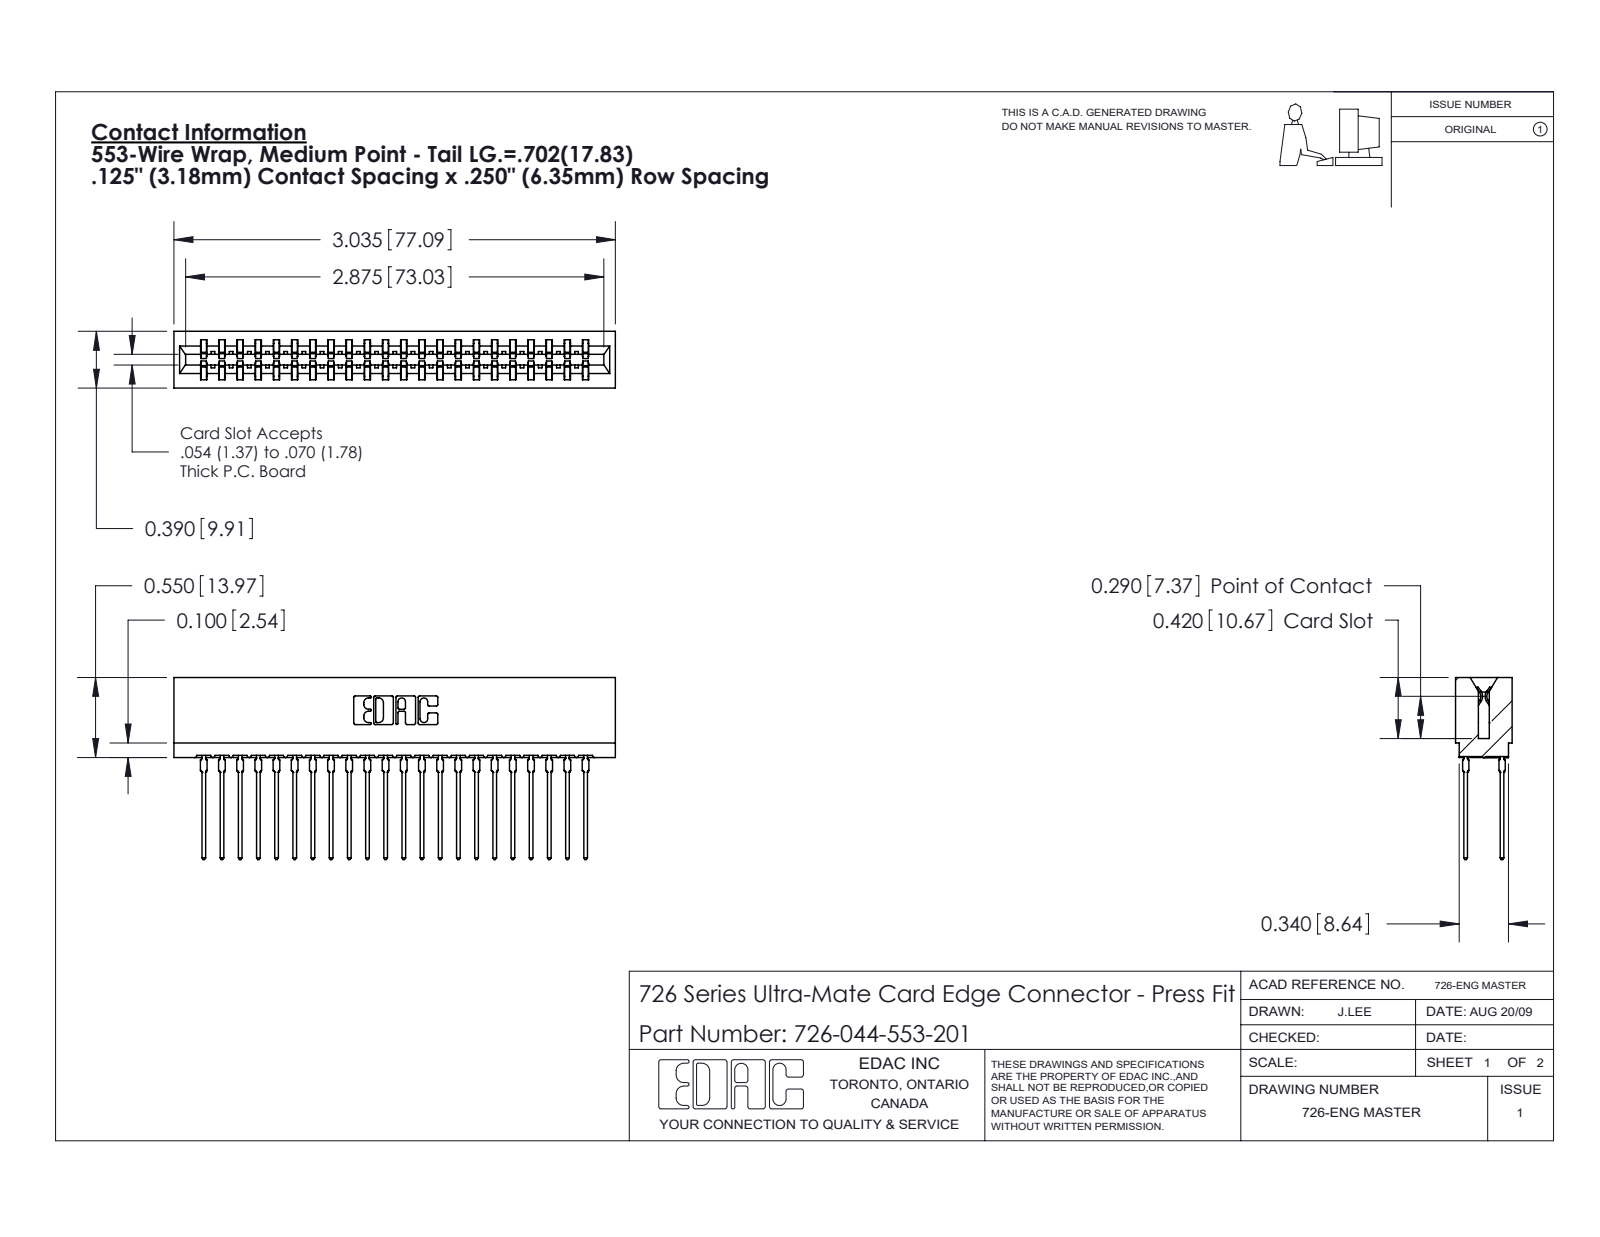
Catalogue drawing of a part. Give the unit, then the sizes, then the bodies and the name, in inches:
Units: inches
Overall size (bounding box): 3.035 × 1.251 × 0.39
Partial cylindrical surfaces — rounded edges, fillets, slot ends (radius × count): R0.021 ×88, R0.015 ×23, R0.01 ×22, R0.005 ×8, R0.011 ×8, R0.007 ×6, R0.031 ×6, R0.026 ×3
Main face-to-face distances: 0.057, 0.333, 0.025, 0.307, 0.25, 0.083, 0.39, 0.275, 0.042, 1.25
Volume: 0.451 in³ · Surface area: 19.94 in²
Bodies: 45 solids, 4035 faces (2079 planar, 812 cylindrical, 1144 other)
Part name (STEP PRODUCT): 746-292-001_553; 726 Part_.515 Slot Depth - 01; 726-044-553-201
STEP written by: SolidWorks 2020 (CONFIG_CONTROL_DESIGN)
